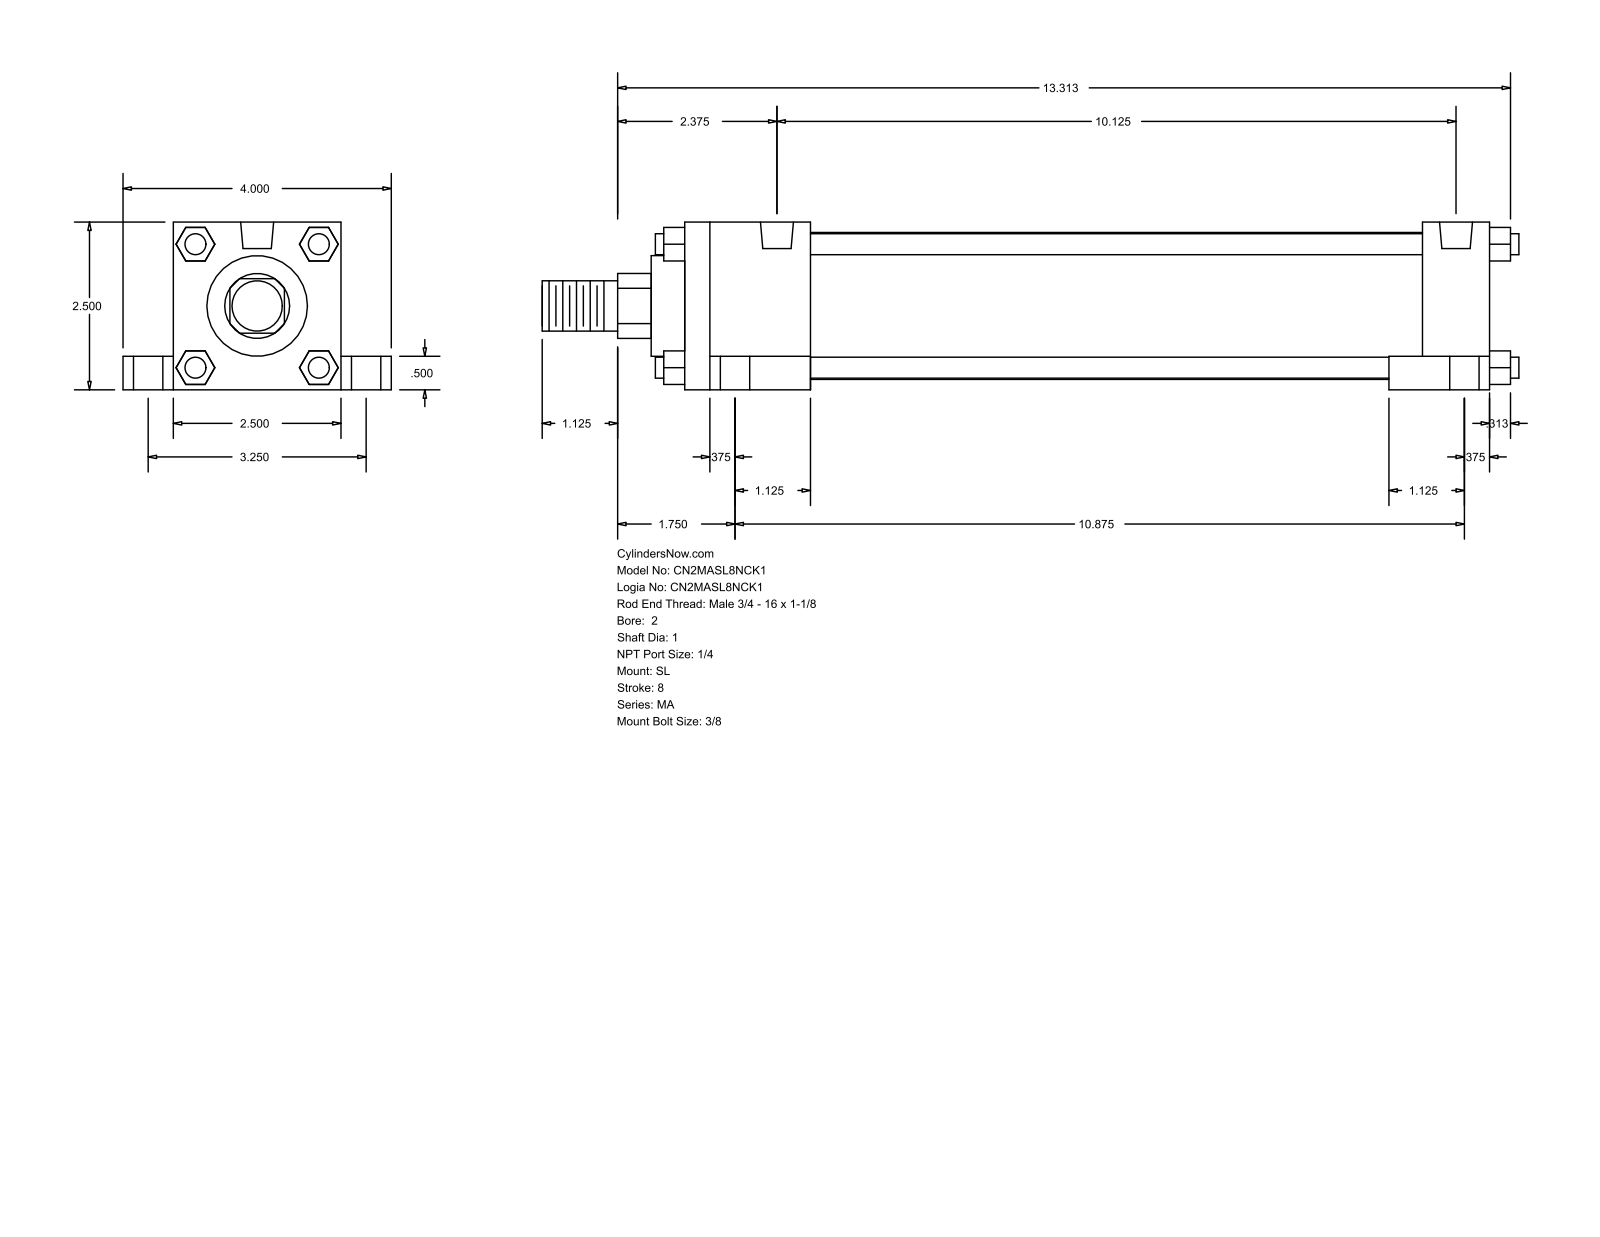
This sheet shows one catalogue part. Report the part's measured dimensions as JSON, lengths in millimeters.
{"part_name": "MA_SL__0200_1", "step_written_by": "GSSL Pune (CONFIG_CONTROL_DESIGN)", "units": "millimeters", "bodies": {"solids": 0, "faces": 148, "planar": 112, "cylindrical": 36, "other": 0}, "overall_size": [369.89, 101.6, 63.5], "round_holes": [[7.94, 4], [11.11, 4], [17.46, 4], [12.49, 2]], "round_bosses_or_shafts": [[7.94, 4], [55.63, 1], [38.1, 1], [25.4, 1], [19.05, 1]], "partial_cylinders_radius": [[12.29, 1]], "face_to_face_distances": [63.5, 12.7, 304.8, 19.05, 82.55, 25.4, 50.8, 47.63, 257.17, 279.4], "hole_center_spacings": [41.39, 44.22, 82.54, 257.17, 263.6, 276.15, 276.23, 288.3]}
